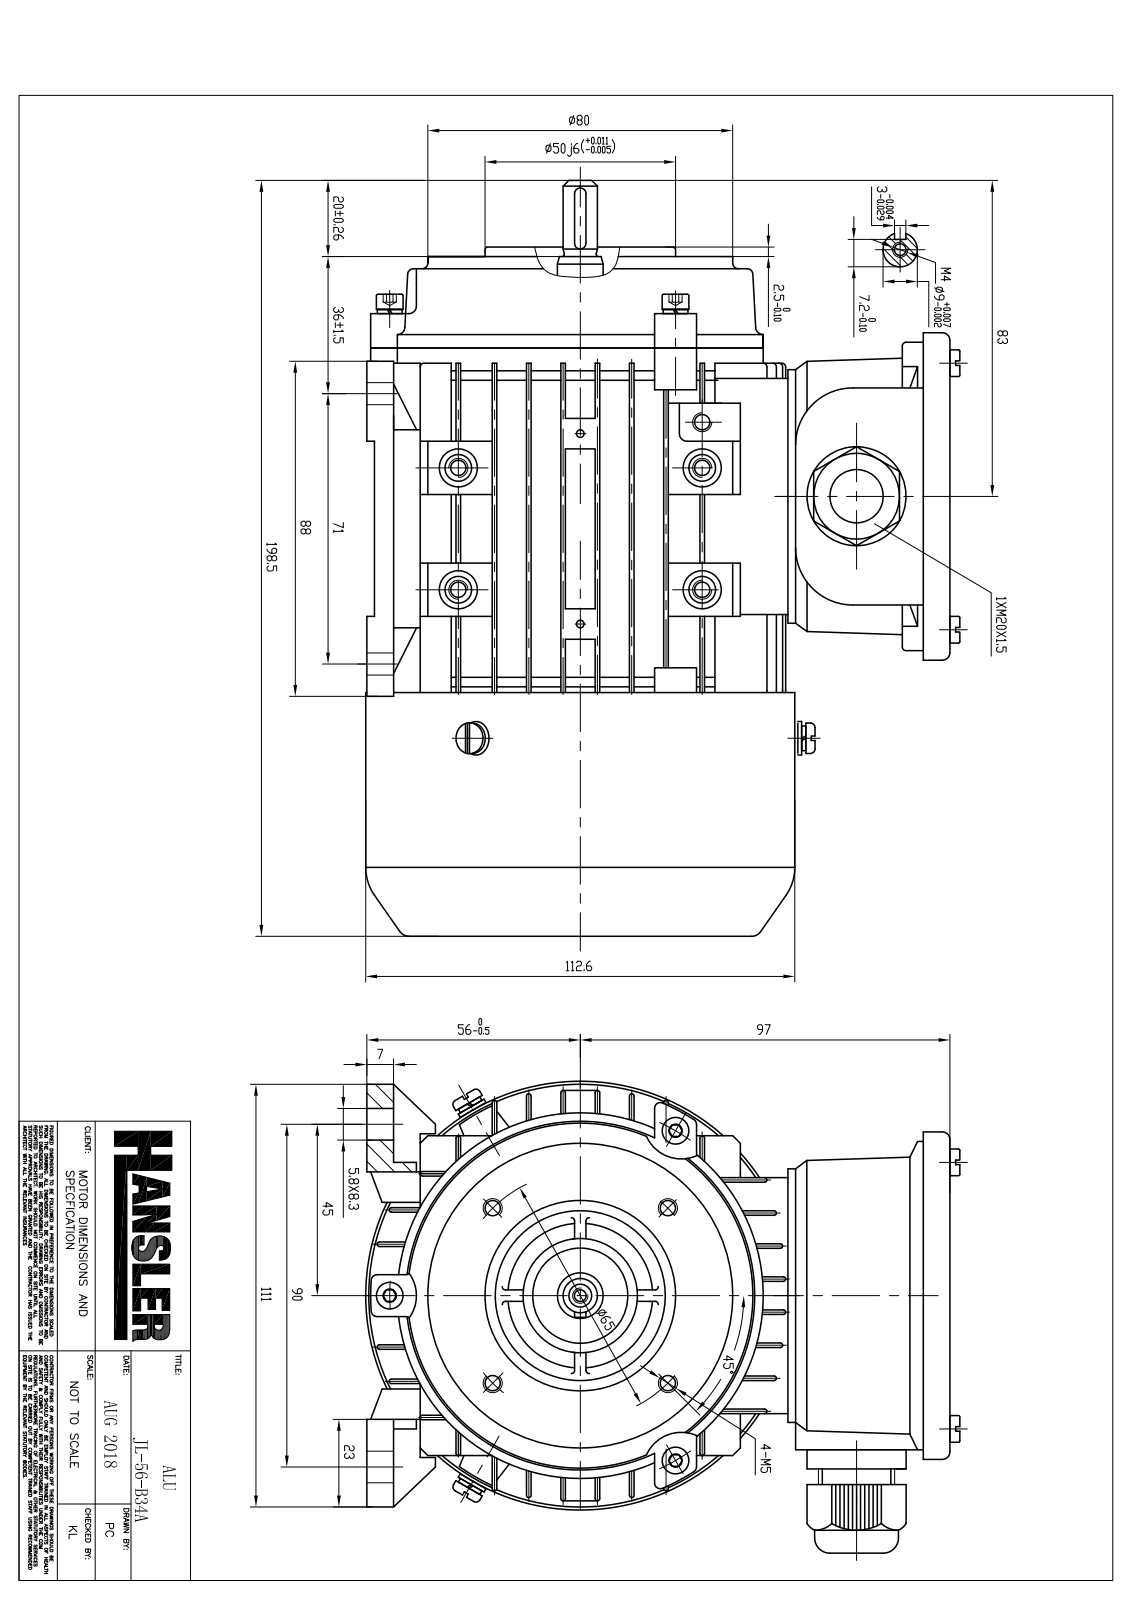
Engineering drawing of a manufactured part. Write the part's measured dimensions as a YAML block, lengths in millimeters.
part_name: "JL-56-B34A"
step_written_by: "SIEMENS PLM Software NX 12.0 (AP203_CONFIGURATION_CONTROLLED_3D_DESIGN_OF_MECHANICAL_PARTS_AND_ASSEMBLIES_MIM_LF)"
units: millimeters
bodies: {solids: 47, faces: 3464, planar: 1878, cylindrical: 1108, other: 478}
overall_size: [198.42, 154.7, 119.88]
volume: 414871
surface_area: 342177
round_holes:
  - {diameter: 4, count: 17}
  - {diameter: 3, count: 14}
  - {diameter: 10, count: 8}
  - {diameter: 4.7, count: 7}
  - {diameter: 4.25, count: 6}
  - {diameter: 4.13, count: 4}
  - {diameter: 5, count: 4}
  - {diameter: 5.25, count: 4}
  - {diameter: 6, count: 4}
  - {diameter: 7.5, count: 4}
  - {diameter: 2, count: 3}
  - {diameter: 4.9, count: 3}
round_bosses_or_shafts:
  - {diameter: 3.55, count: 10}
  - {diameter: 7, count: 8}
  - {diameter: 6.45, count: 6}
  - {diameter: 4, count: 6}
  - {diameter: 10, count: 4}
  - {diameter: 9.5, count: 4}
  - {diameter: 8.5, count: 4}
  - {diameter: 7.85, count: 4}
partial_cylinders:
  - {radius: 0.5, count: 280}
  - {radius: 1, count: 53}
  - {radius: 2, count: 47}
  - {radius: 3, count: 36}
  - {radius: 5, count: 20}
  - {radius: 1.5, count: 14}
  - {radius: 6, count: 12}
  - {radius: 2.9, count: 8}
face_to_face_distances: [8.68, 17.36, 2, 26.04, 1.2, 34.72, 9.88, 7.48, 4, 27.24]
hole_center_spacings: [44, 58.46, 32, 50, 12, 17.63, 18.38, 25.81]
